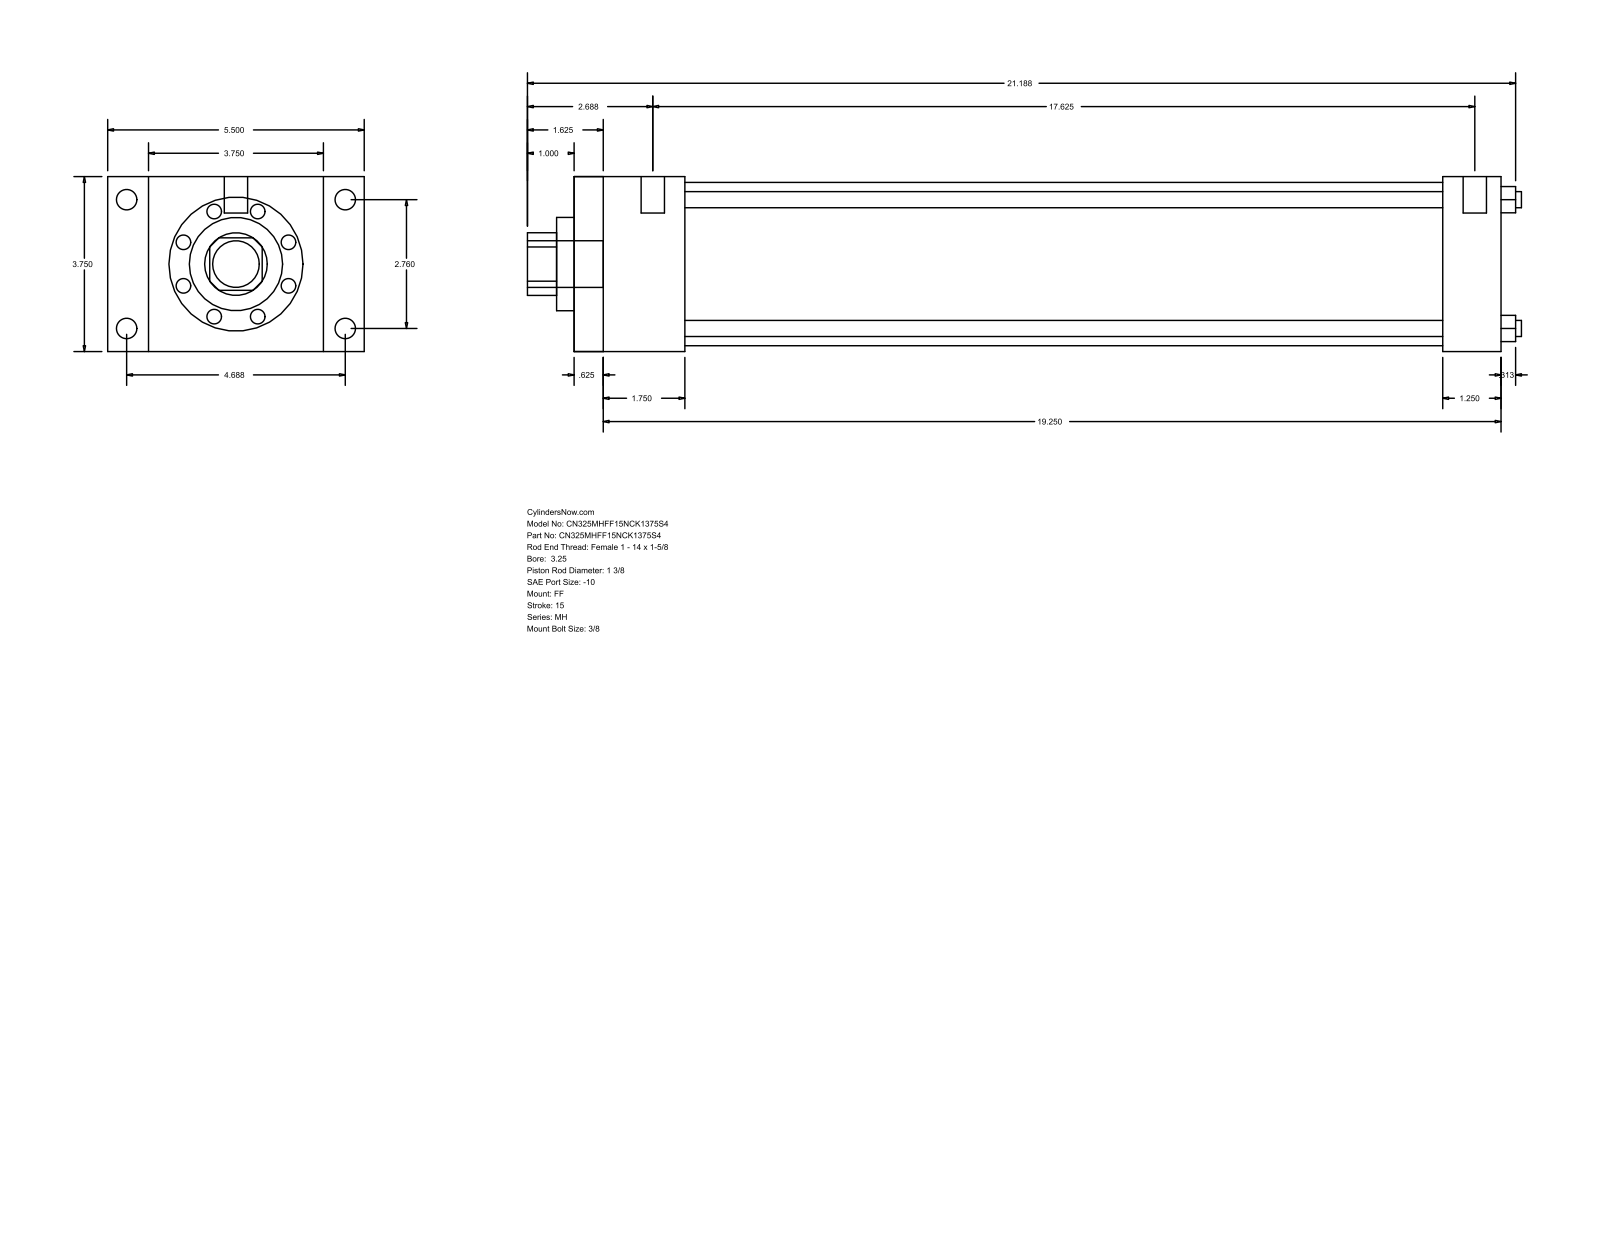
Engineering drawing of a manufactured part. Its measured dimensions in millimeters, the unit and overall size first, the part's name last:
Units: millimetres
Overall size (bounding box): 541.34 × 139.7 × 95.25
Round holes (diameter × count): ⌀8.76 ×4, ⌀34.92 ×1, ⌀50.8 ×1, ⌀88.9 ×1
Round bosses / shafts (diameter × count): ⌀11.13 ×4, ⌀5.56 ×4, ⌀12.7 ×2, ⌀25.4 ×1
Partial cylindrical surfaces — rounded edges, fillets, slot ends (radius × count): R17.06 ×1
Main face-to-face distances: 95.24, 504.83, 15.87, 488.96, 22.23, 117.47, 473.08, 457.21, 31.75, 60.32
Hole centre spacings: 49.57, 70.1, 99.14
Bodies: 0 solids, 92 faces (64 planar, 28 cylindrical, 0 other)
Part name (STEP PRODUCT): MH_FF__0325_1.375
STEP written by: GSSL Pune (CONFIG_CONTROL_DESIGN)
